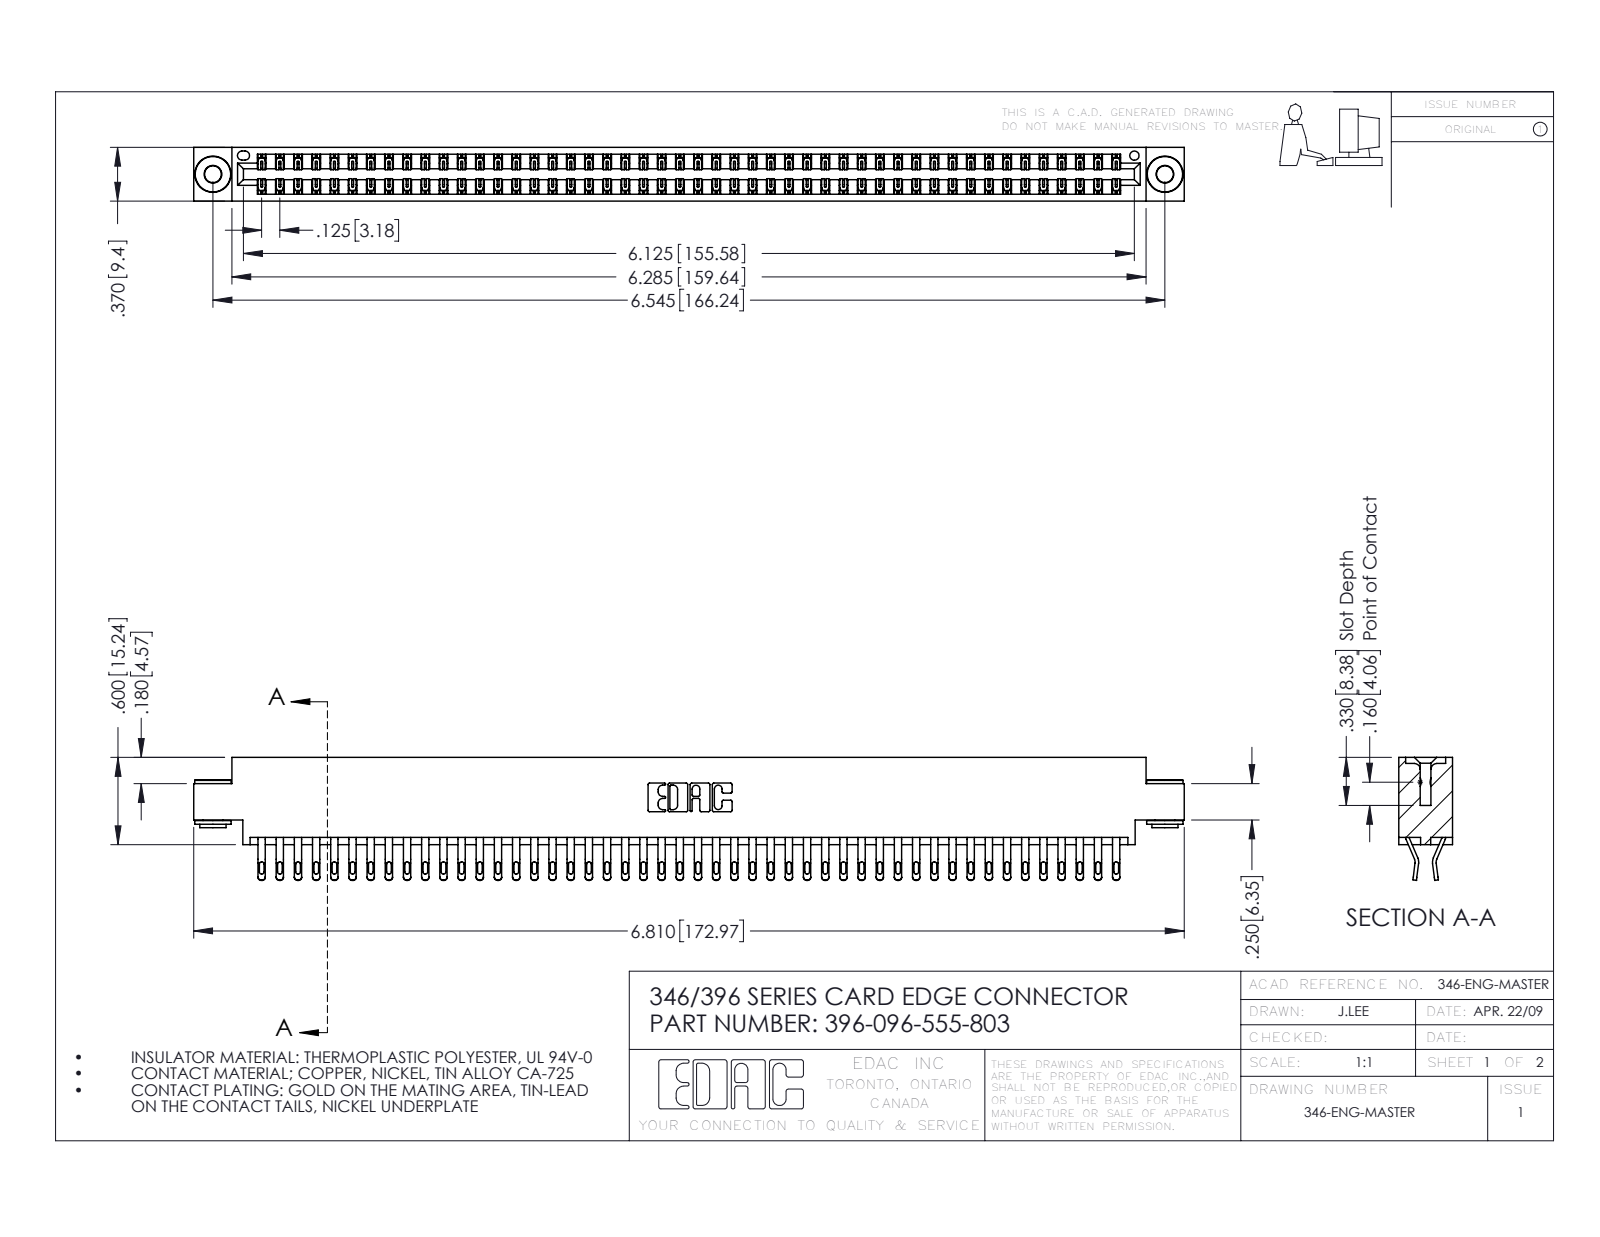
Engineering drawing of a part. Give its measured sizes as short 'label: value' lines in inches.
name: 396-096-555-803; 345-250-002_345-250-002-102; 345-292-001_555 Tail; 346 Part_0.170 Offset - 0.156 Dia-TH
written by: SolidWorks 2016 (CONFIG_CONTROL_DESIGN)
unit: in
bodies: 99 solids, 5732 faces (3258 planar, 2466 cylindrical, 8 other)
size: 6.81 × 0.845 × 0.37
volume: 1.041 in³; area: 38.64 in²
holes: 2× ⌀0.116, 2× ⌀0.156, 1× ⌀0.064
bosses: 2× ⌀0.25, 2× ⌀0.18, 2× ⌀0.136
rounds: 192× R0.016, 192× R0.02, 144× R0.006, 22× R0.01, 6× R0.007, 6× R0.031, 3× R0.026, 2× R0.01
face distances: 0.048, 0.322, 0.37, 0.25, 0.025, 0.275, 0.072, 0.298, 0.148, 0.222
hole spacings: 0.246, 6.336, 6.545
